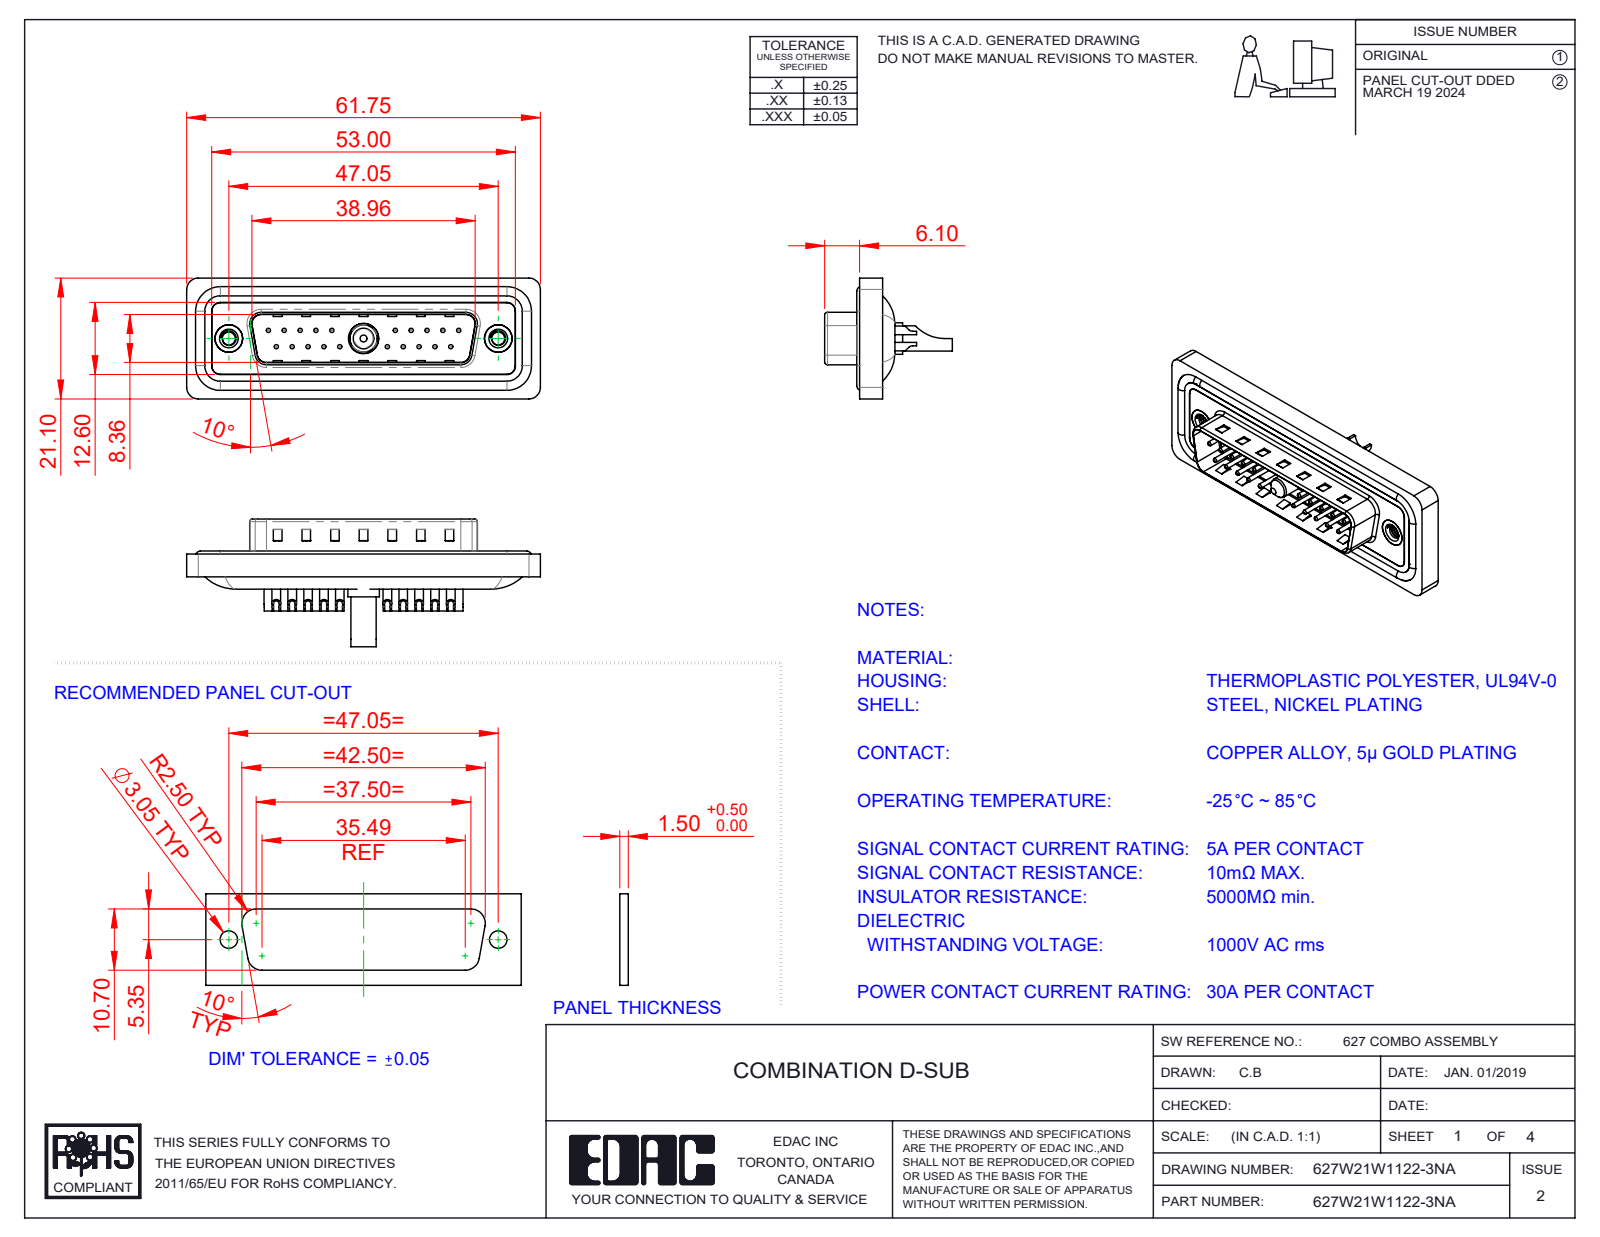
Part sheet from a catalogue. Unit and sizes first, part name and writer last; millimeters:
Units: millimetres
Overall size (bounding box): 61.75 × 22.3 × 21.1
Round holes (diameter × count): ⌀0.75 ×20, ⌀1 ×20, ⌀1.6 ×20, ⌀2 ×20, ⌀2.26 ×2, ⌀4 ×2, ⌀4.8 ×2, ⌀5 ×2, ⌀3.5 ×1, ⌀4.85 ×1, ⌀5.3 ×1
Round bosses / shafts (diameter × count): ⌀1.5 ×20, ⌀1.6 ×4, ⌀4.9 ×2, ⌀5.5 ×1, ⌀5.2 ×1, ⌀4.75 ×1, ⌀4.4 ×1, ⌀3.75 ×1
Partial cylindrical surfaces — rounded edges, fillets, slot ends (radius × count): R1.5 ×22, R2 ×18, R0.5 ×8, R1.6 ×8, R1 ×6, R0.25 ×4, R0.6 ×4, R0.65 ×4
Main face-to-face distances: 0.4, 1.5, 1.1, 1.6, 0.5, 3.1, 2.9, 4.1, 0.82, 9.58
Hole centre spacings: 3.16, 2.77, 5.54, 8.31, 5.04, 19.39, 20.97, 22.16
Volume: 7 254 mm³ · Surface area: 12 218 mm²
Bodies: 29 solids, 1266 faces (402 planar, 532 cylindrical, 332 other)
Part name (STEP PRODUCT): 627Combo Threaded Rivet_A; 627Combo Shell Front_25 Contacts; Power Pin_30A SC; 627Combo Contact Row 1_22 (+5 more)
STEP written by: SolidWorks 2023 (CONFIG_CONTROL_DESIGN)
